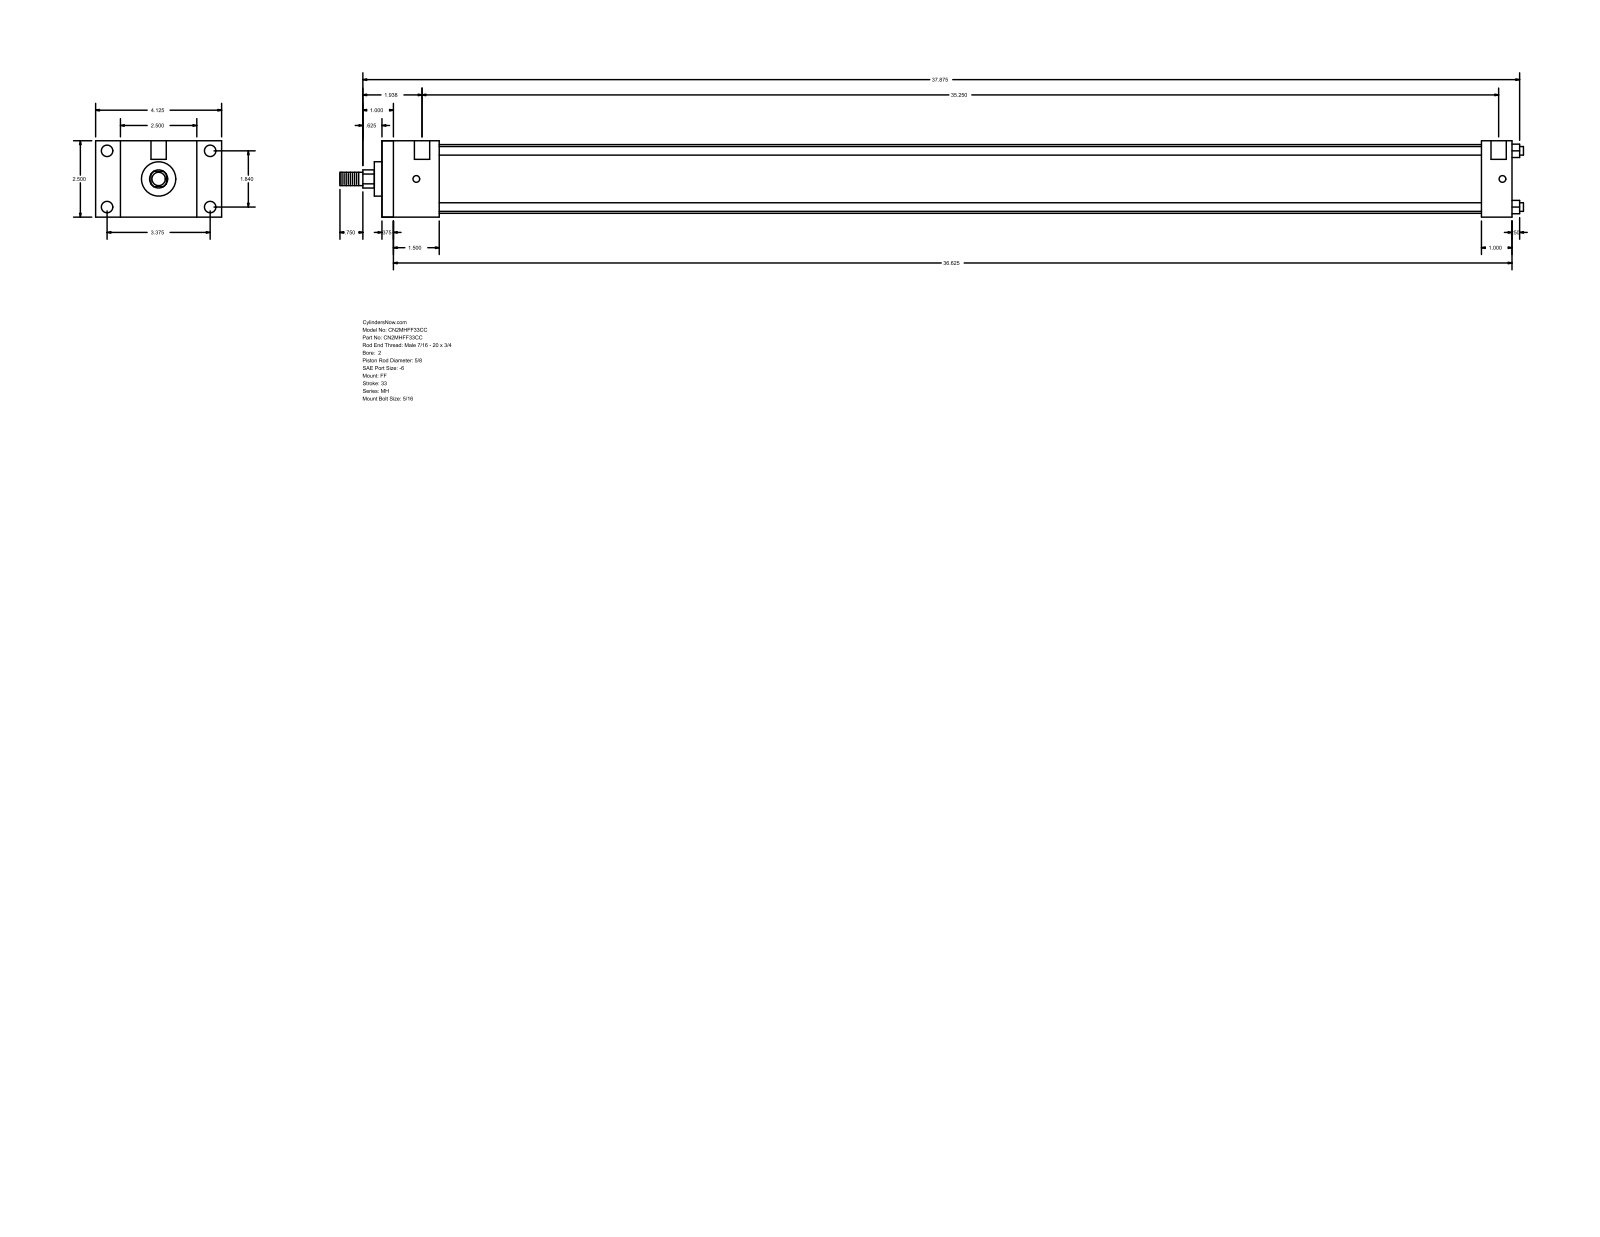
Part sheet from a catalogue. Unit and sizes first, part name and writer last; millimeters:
Units: millimetres
Overall size (bounding box): 984.25 × 104.78 × 63.5
Round holes (diameter × count): ⌀5.56 ×4, ⌀9.53 ×4, ⌀12.7 ×2
Round bosses / shafts (diameter × count): ⌀7.14 ×4, ⌀57.15 ×1, ⌀28.57 ×1, ⌀15.88 ×1, ⌀11.11 ×1
Partial cylindrical surfaces — rounded edges, fillets, slot ends (radius × count): R7.54 ×1
Main face-to-face distances: 63.5, 939.79, 930.27, 9.52, 25.4, 38.1, 47.62, 914.39, 904.87, 866.77
Hole centre spacings: 46.74, 85.72, 97.63, 903.29, 3.18, 4.76, 895.35, 898.53
Bodies: 0 solids, 92 faces (64 planar, 28 cylindrical, 0 other)
Part name (STEP PRODUCT): MH_FF__0200_0.625
STEP written by: GSSL Pune (CONFIG_CONTROL_DESIGN)
